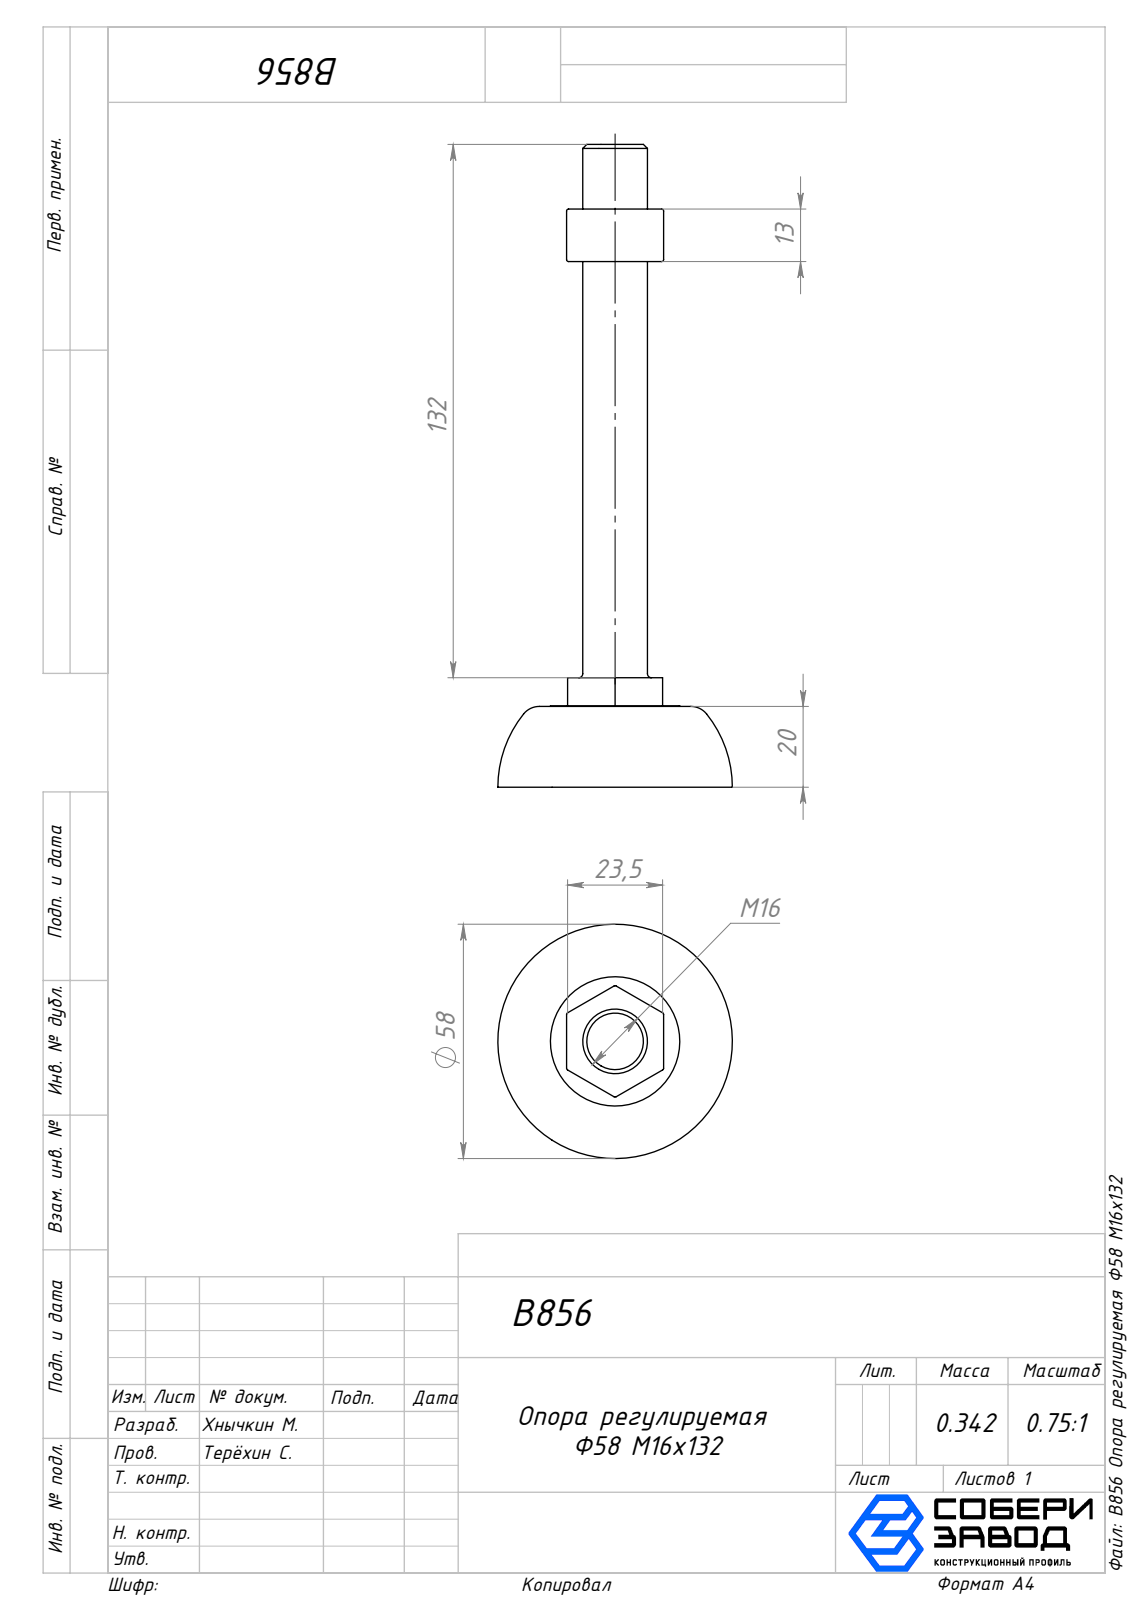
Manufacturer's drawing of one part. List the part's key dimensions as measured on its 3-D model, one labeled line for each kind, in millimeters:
Part name (STEP PRODUCT): Гайка_00; Мал. гайка_00; Опора_00; B856 Опора регулируемая Ф58 М16х132 (+1 more)
STEP written by: SolidWorks 2025 (AUTOMOTIVE_DESIGN)
Units: millimetres
Bodies: 4 solids, 123 faces (30 planar, 48 cylindrical, 45 other)
Overall size (bounding box): 159.1 × 58 × 58
Volume: 48 448 mm³ · Surface area: 20 337 mm²
Round holes (diameter × count): ⌀4 ×1, ⌀5 ×1, ⌀14 ×1
Round bosses / shafts (diameter × count): ⌀32 ×1, ⌀16 ×1
Partial cylindrical surfaces — rounded edges, fillets, slot ends (radius × count): R0.5 ×36
Main face-to-face distances: 19.9, 20.1, 23.75, 24, 7, 20, 23.5, 143.1, 123.2, 123.1
